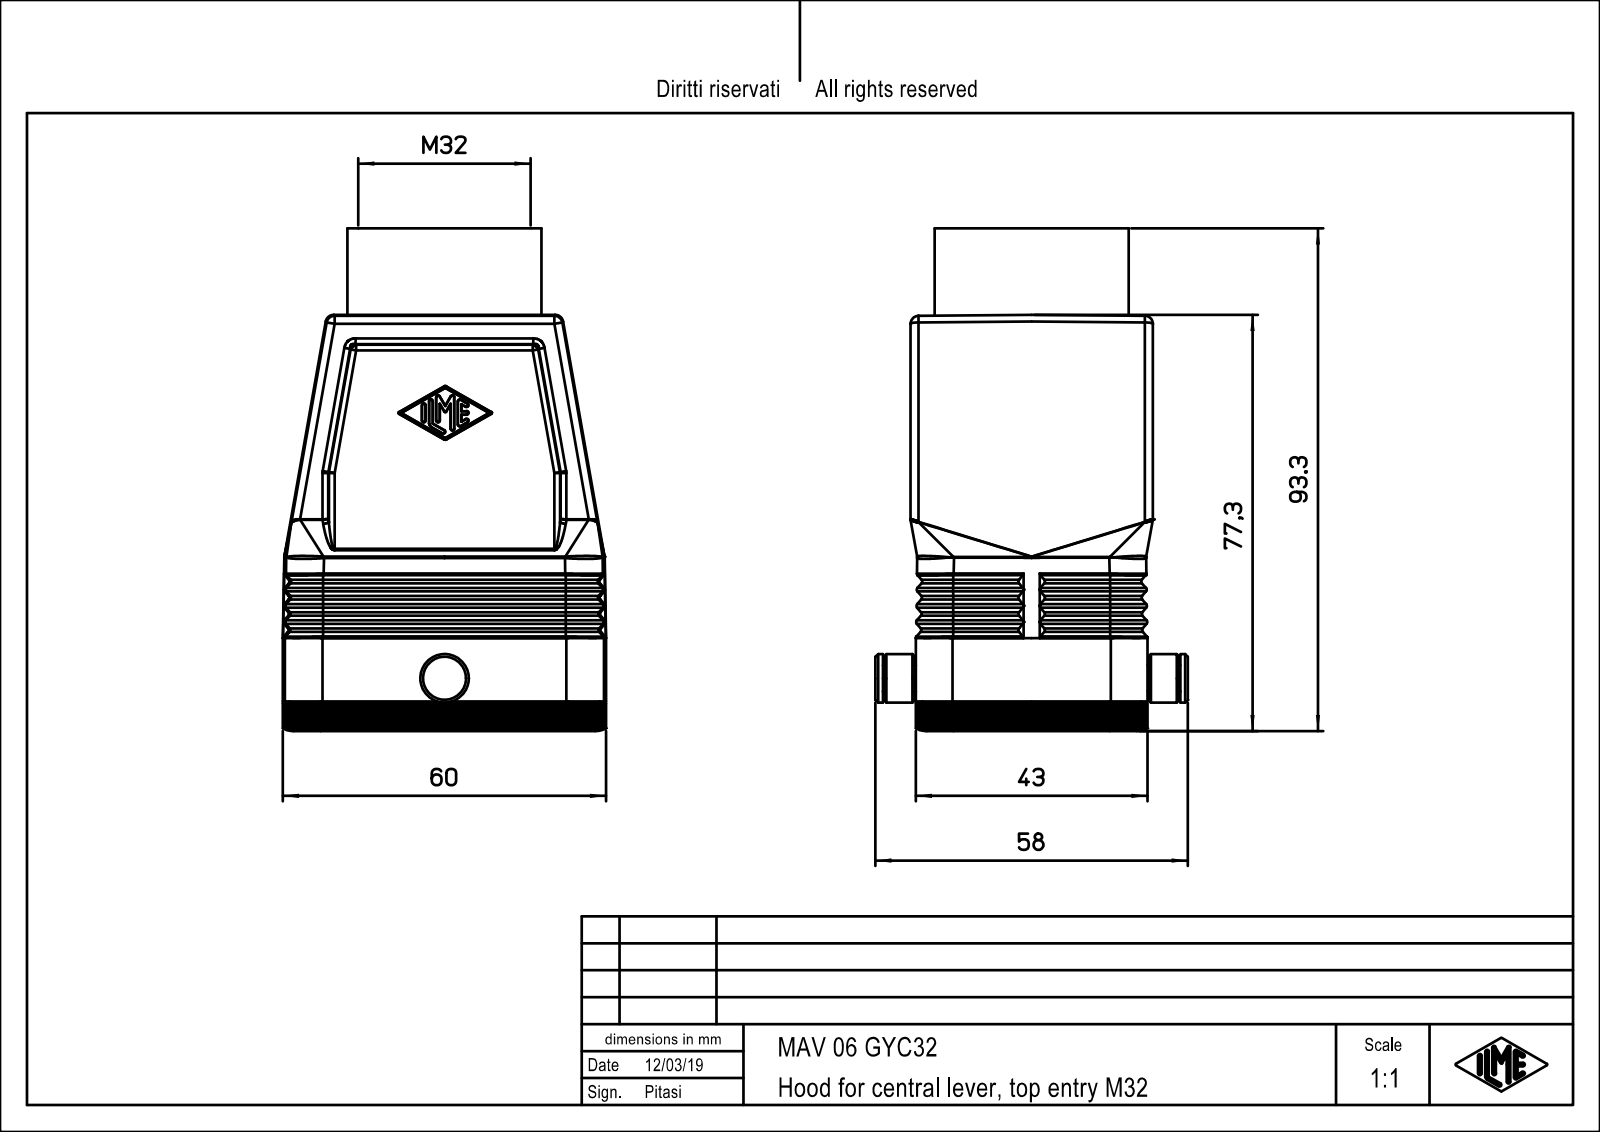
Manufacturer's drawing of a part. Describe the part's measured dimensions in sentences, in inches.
The part is named "MAV_06_GYC32". Its 3-D file was written by "PTC Creo Elements/Direct Modeling 19.0E 27-Jun-2016 (C) Parametric Technology GmbH (AUTOMOTIVE_DESIGN)". It is 1 solid with 524 faces: 168 planar, 176 cylindrical and 180 other. Overall it measures 3.671 by 2.362 by 2.283 inches. Its volume is 4.222 cubic inches and its surface area 56.13 square inches. Round holes: 4 of diameter 0.118, 1 of diameter 1.063. Round bosses or shafts: 1 of diameter 1.417, 1 of diameter 1.26, 1 of diameter 0.354, 1 of diameter 0.189. Partial cylindrical surfaces (rounded edges, fillets, slot ends): 54 of radius 0.02, 44 of radius 0.059, 12 of radius 0.118, 12 of radius 0.276, 4 of radius 0.157, 4 of radius 0.165, 4 of radius 0.228. The main face-to-face distances are 1.693, 0.079, 0.276, 0.157, 0.297, 0.039, 1.732, 2.362, 1.535, 0.315. The hole center spacings are 1.016, 1.063, 1.732, 2.032.
